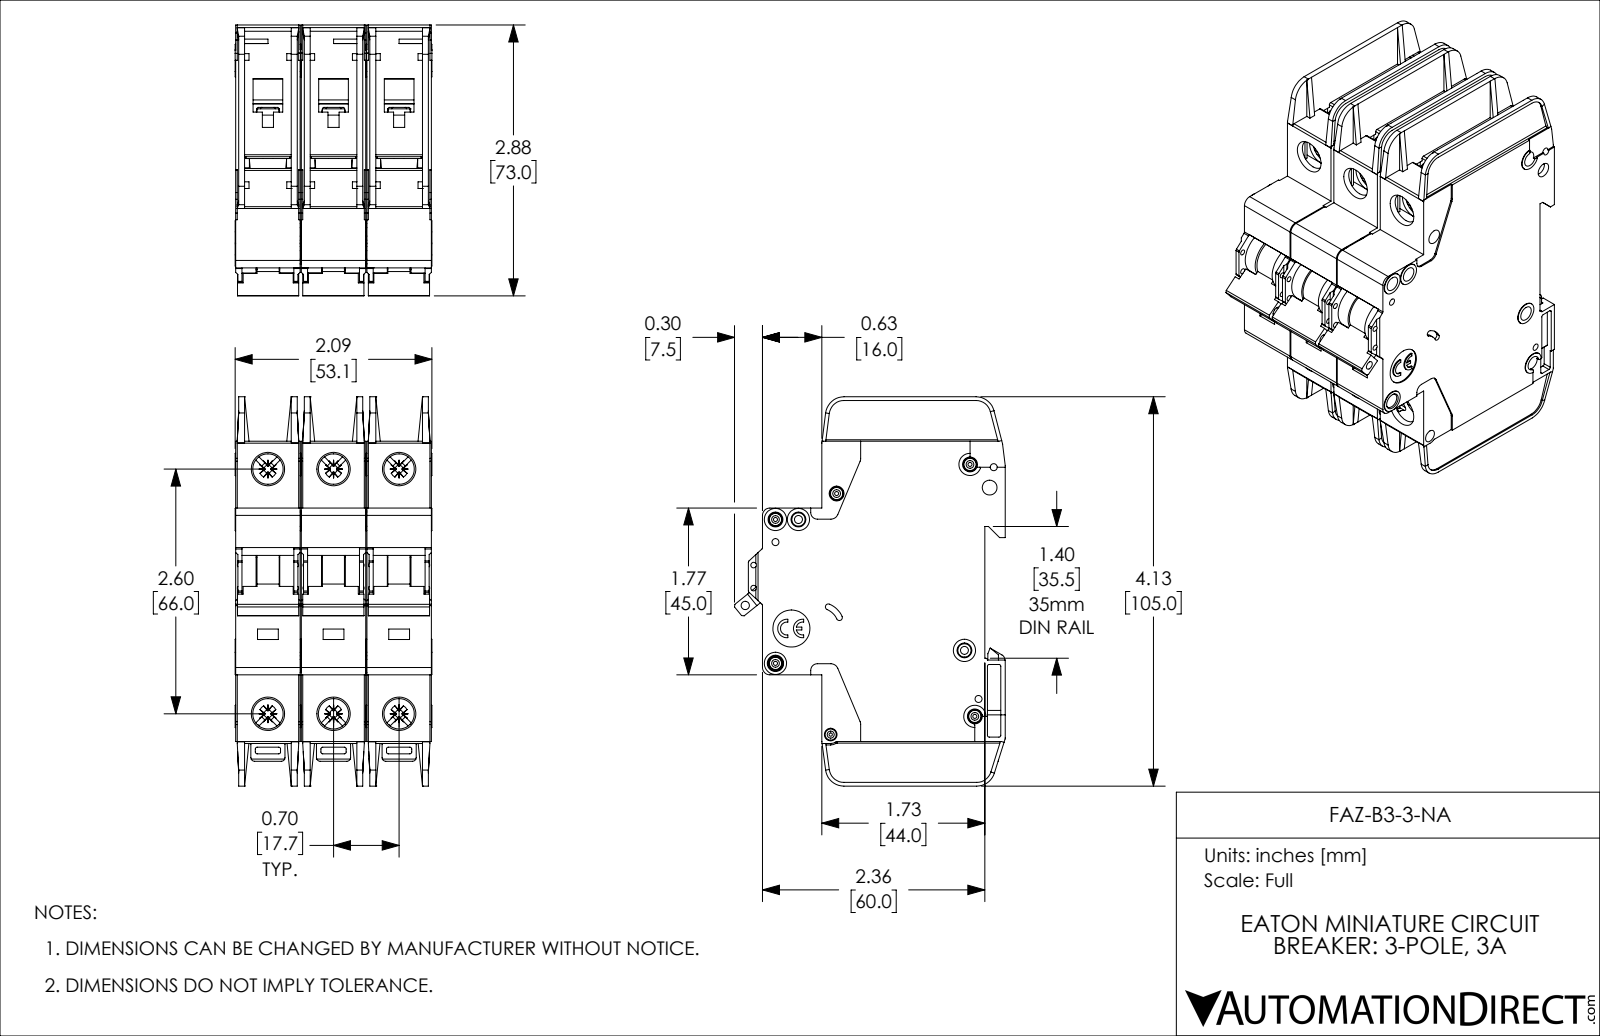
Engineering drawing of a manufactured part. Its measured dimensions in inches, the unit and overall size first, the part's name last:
Units: inches
Overall size (bounding box): 4.134 × 2.876 × 2.091
Round holes (diameter × count): ⌀0.157 ×8, ⌀0.323 ×6, ⌀0.043 ×5, ⌀0.075 ×4, ⌀0.059 ×2, ⌀0.085 ×2, ⌀0.035 ×1, ⌀0.089 ×1, ⌀0.098 ×1, ⌀0.134 ×1, ⌀0.394 ×1
Round bosses / shafts (diameter × count): ⌀0.13 ×5, ⌀0.236 ×4, ⌀0.118 ×4, ⌀0.098 ×3
Partial cylindrical surfaces — rounded edges, fillets, slot ends (radius × count): R0.02 ×72, R0.016 ×30, R0.039 ×18, R0.043 ×12, R0.079 ×12, R0.008 ×6, R0.01 ×6, R0.028 ×6
Main face-to-face distances: 0.697, 0.047, 1.394, 0.685, 0.591, 1.382, 0.744, 0.65, 0.106, 0.094
Hole centre spacings: 0.697, 2.69, 2.598, 0.244, 0.537, 0.87, 1.394, 2.948
Volume: 14.05 in³ · Surface area: 123 in²
Bodies: 3 solids, 3381 faces (2013 planar, 1071 cylindrical, 297 other)
Part name (STEP PRODUCT): FAZ-B3-3-NA
STEP written by: SolidWorks 2019 (AUTOMOTIVE_DESIGN)
